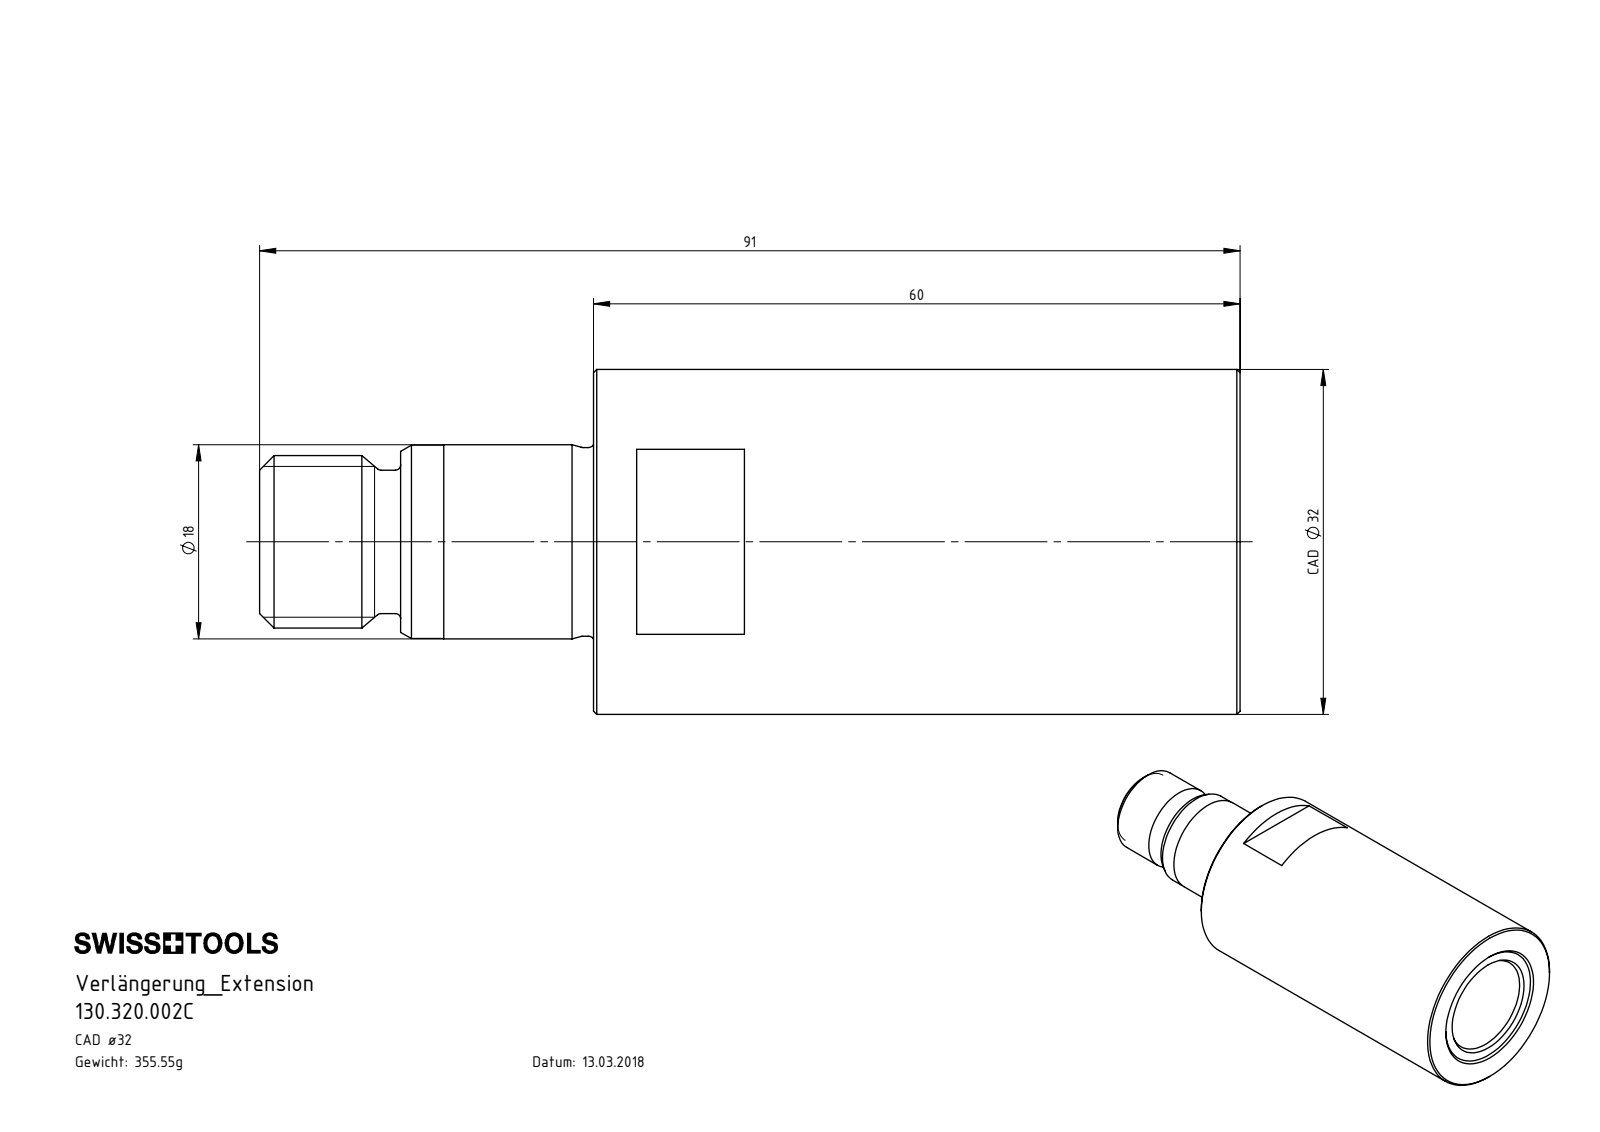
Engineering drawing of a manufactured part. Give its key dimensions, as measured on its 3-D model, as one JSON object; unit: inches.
{"part_name": "130.320.002C", "step_written_by": "SolidWorks 2017 (CONFIG_CONTROL_DESIGN)", "units": "inches", "bodies": {"solids": 1, "faces": 71, "planar": 13, "cylindrical": 20, "other": 38}, "overall_size": [3.583, 1.26, 1.26], "volume_in3": 2.764, "surface_area_in2": 18.59, "round_holes": [[0.165, 1], [0.551, 1], [0.709, 1], [0.728, 1]], "round_bosses_or_shafts": [[1.26, 1], [0.707, 1], [0.689, 1], [0.63, 1], [0.524, 1]], "face_to_face_distances": [2.362, 1.063, 1.22, 3.583, 3.567, 2.346, 0.016, 0.705, 0.516, 3.051]}
